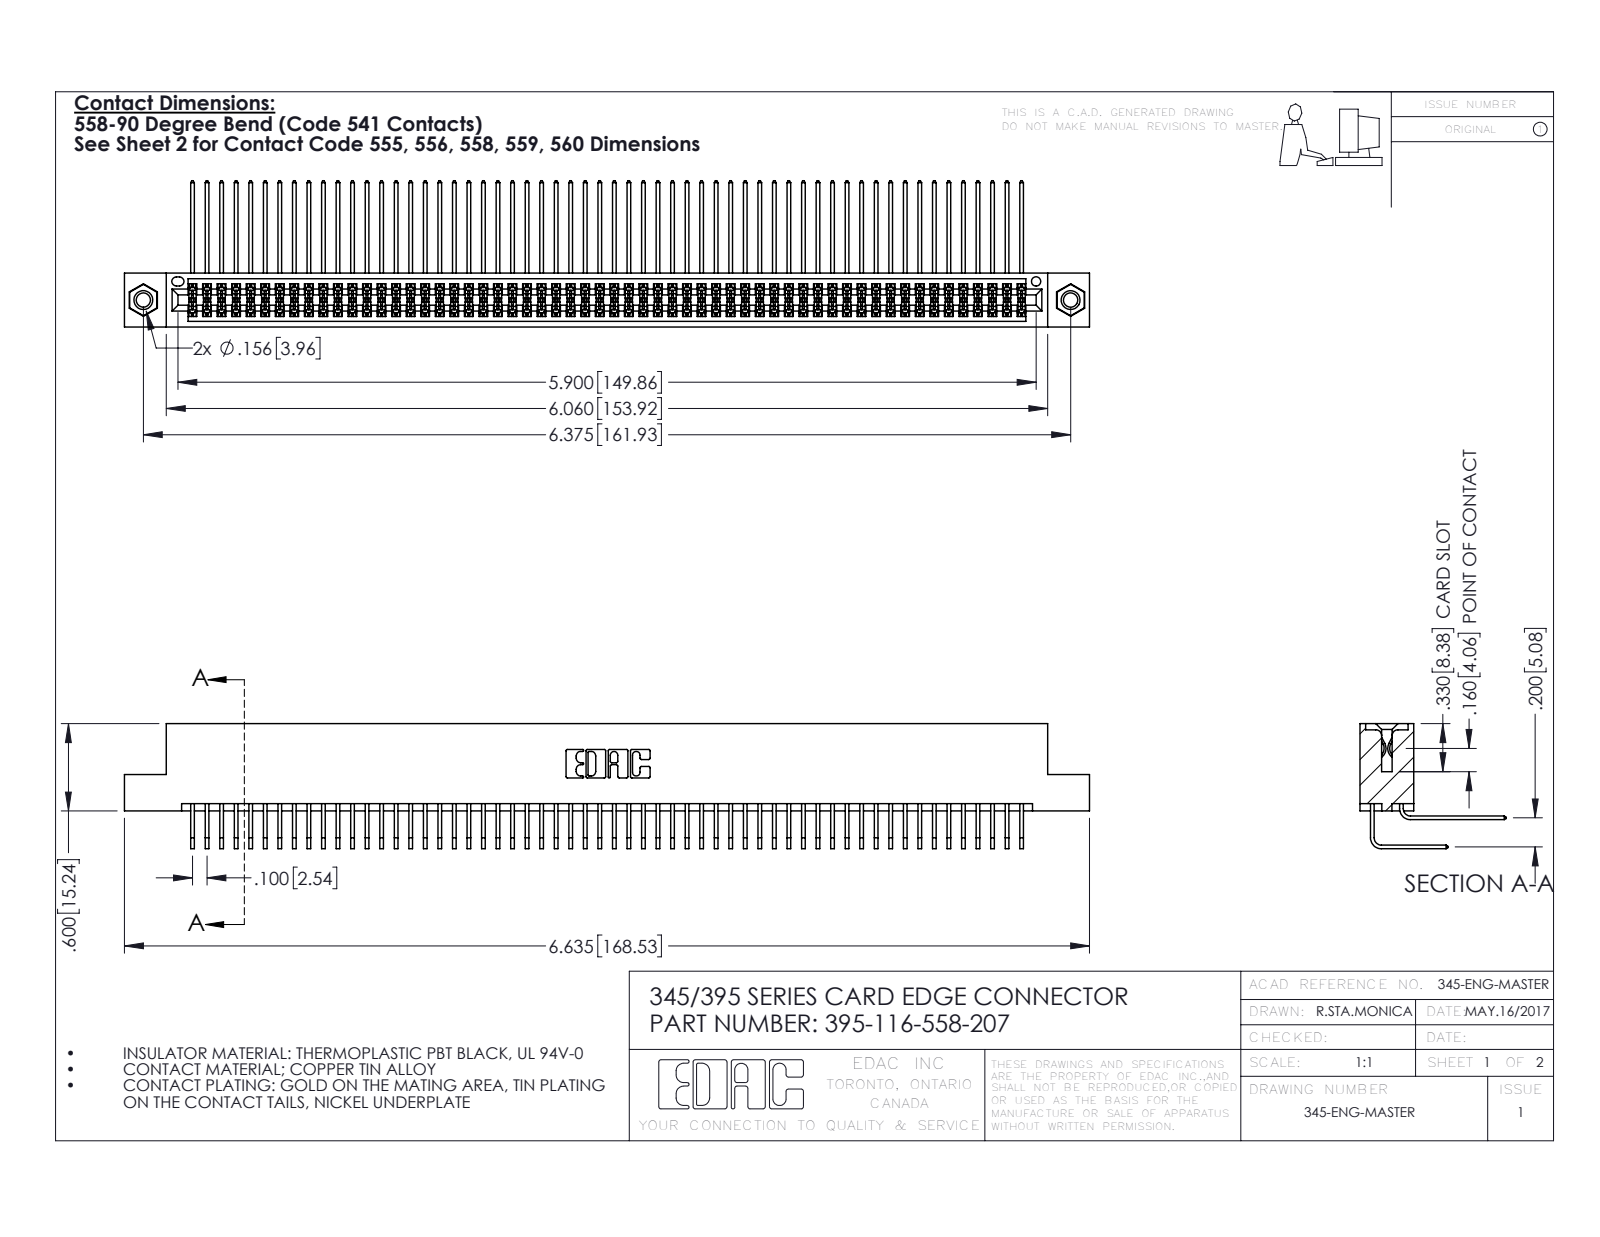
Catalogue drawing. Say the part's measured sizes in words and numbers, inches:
The part is named "345 Part_Flush Mounting Lugs - 0.156 Dia-TI; 395-116-558-207; 345-250-001_345-250-005-103; 345-292-001_558 Tail - 2 (+1 more)". Its 3-D file was written by "SolidWorks 2016 (CONFIG_CONTROL_DESIGN)". It is 119 solids with 6218 faces: 4172 planar, 2030 cylindrical and 16 other. Overall it measures 6.635 by 1.005 by 0.859 inches. Its volume is 1.048 cubic inches and its surface area 44.75 square inches. Round holes: 2 of diameter 0.098, 2 of diameter 0.125, 2 of diameter 0.156, 1 of diameter 0.064. Round bosses or shafts: 2 of diameter 0.155. Partial cylindrical surfaces (rounded edges, fillets, slot ends): 174 of radius 0.006, 22 of radius 0.01, 6 of radius 0.007, 6 of radius 0.031, 3 of radius 0.026, 2 of radius 0.014, 2 of radius 0.019, 2 of radius 0.022. The main face-to-face distances are 0.072, 0.298, 0.2, 0.37, 0.098, 0.272, 0.025, 0.225, 0.025, 0.175. The hole center spacings are 0.27, 6.139, 6.375.
